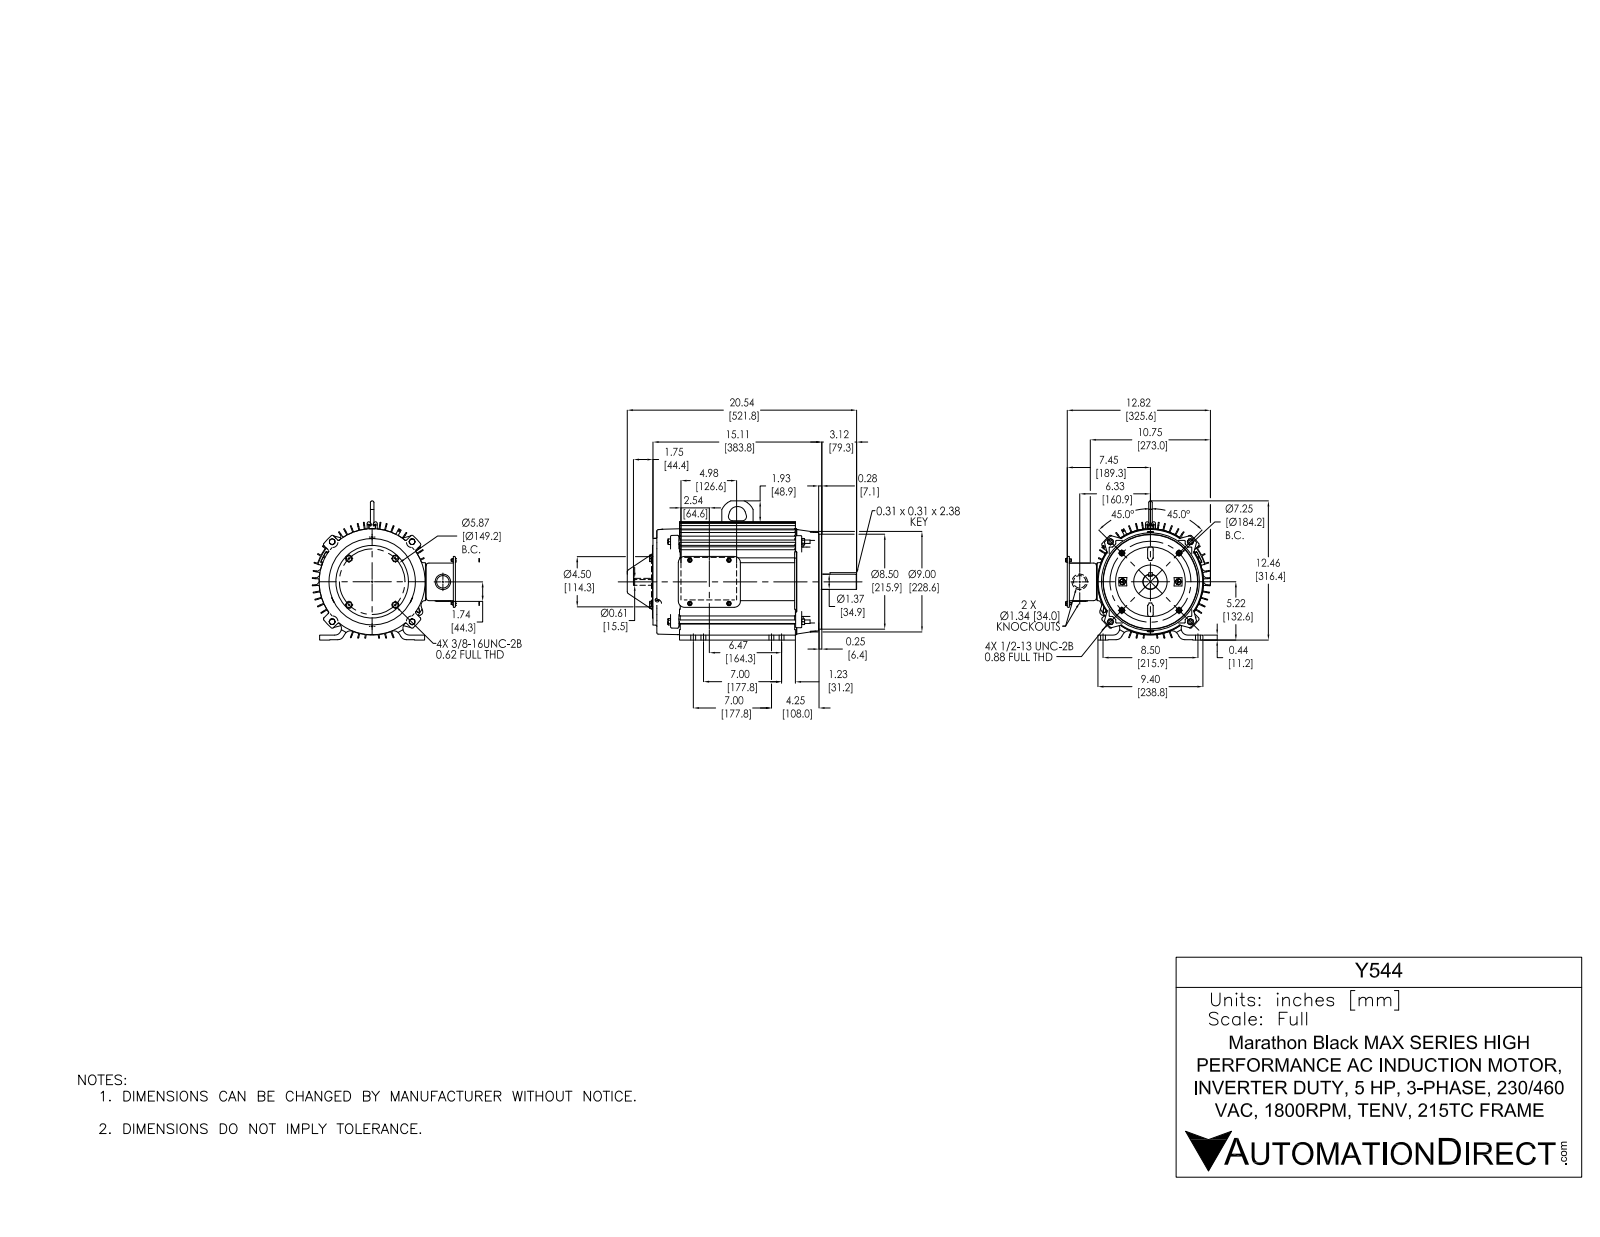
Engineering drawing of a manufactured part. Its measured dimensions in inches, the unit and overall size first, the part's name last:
Units: inches
Overall size (bounding box): 20.542 × 12.957 × 12.456
Round holes (diameter × count): ⌀0.437 ×8, ⌀0.343 ×6, ⌀0.174 ×4, ⌀0.219 ×4, ⌀0.257 ×4, ⌀0.31 ×4, ⌀0.312 ×4, ⌀0.406 ×4, ⌀0.422 ×4, ⌀0.175 ×2, ⌀0.175 ×2, ⌀0.25 ×2
Round bosses / shafts (diameter × count): ⌀0.31 ×6, ⌀0.5 ×4, ⌀0.399 ×4, ⌀0.295 ×4, ⌀0.19 ×4, ⌀0.44 ×2, ⌀0.375 ×2, ⌀0.375 ×2
Partial cylindrical surfaces — rounded edges, fillets, slot ends (radius × count): R0.06 ×162, R0.12 ×130, R0.038 ×32, R0.25 ×25, R0.03 ×19, R0.19 ×12, R0.095 ×8, R0.25 ×8
Main face-to-face distances: 0.076, 0.06, 2.622, 0.1, 2.734, 15.111, 2.682, 2.56, 0.25, 0.03
Hole centre spacings: 4.666, 5.853, 6.227, 2.12, 4, 0.688, 0.91, 1.437
Volume: 243.8 in³ · Surface area: 2 437 in²
Bodies: 34 solids, 3696 faces (1026 planar, 1023 cylindrical, 1647 other)
Part name (STEP PRODUCT): SS330203-1025_Rev3
STEP written by: SolidWorks 2017 (AUTOMOTIVE_DESIGN)
